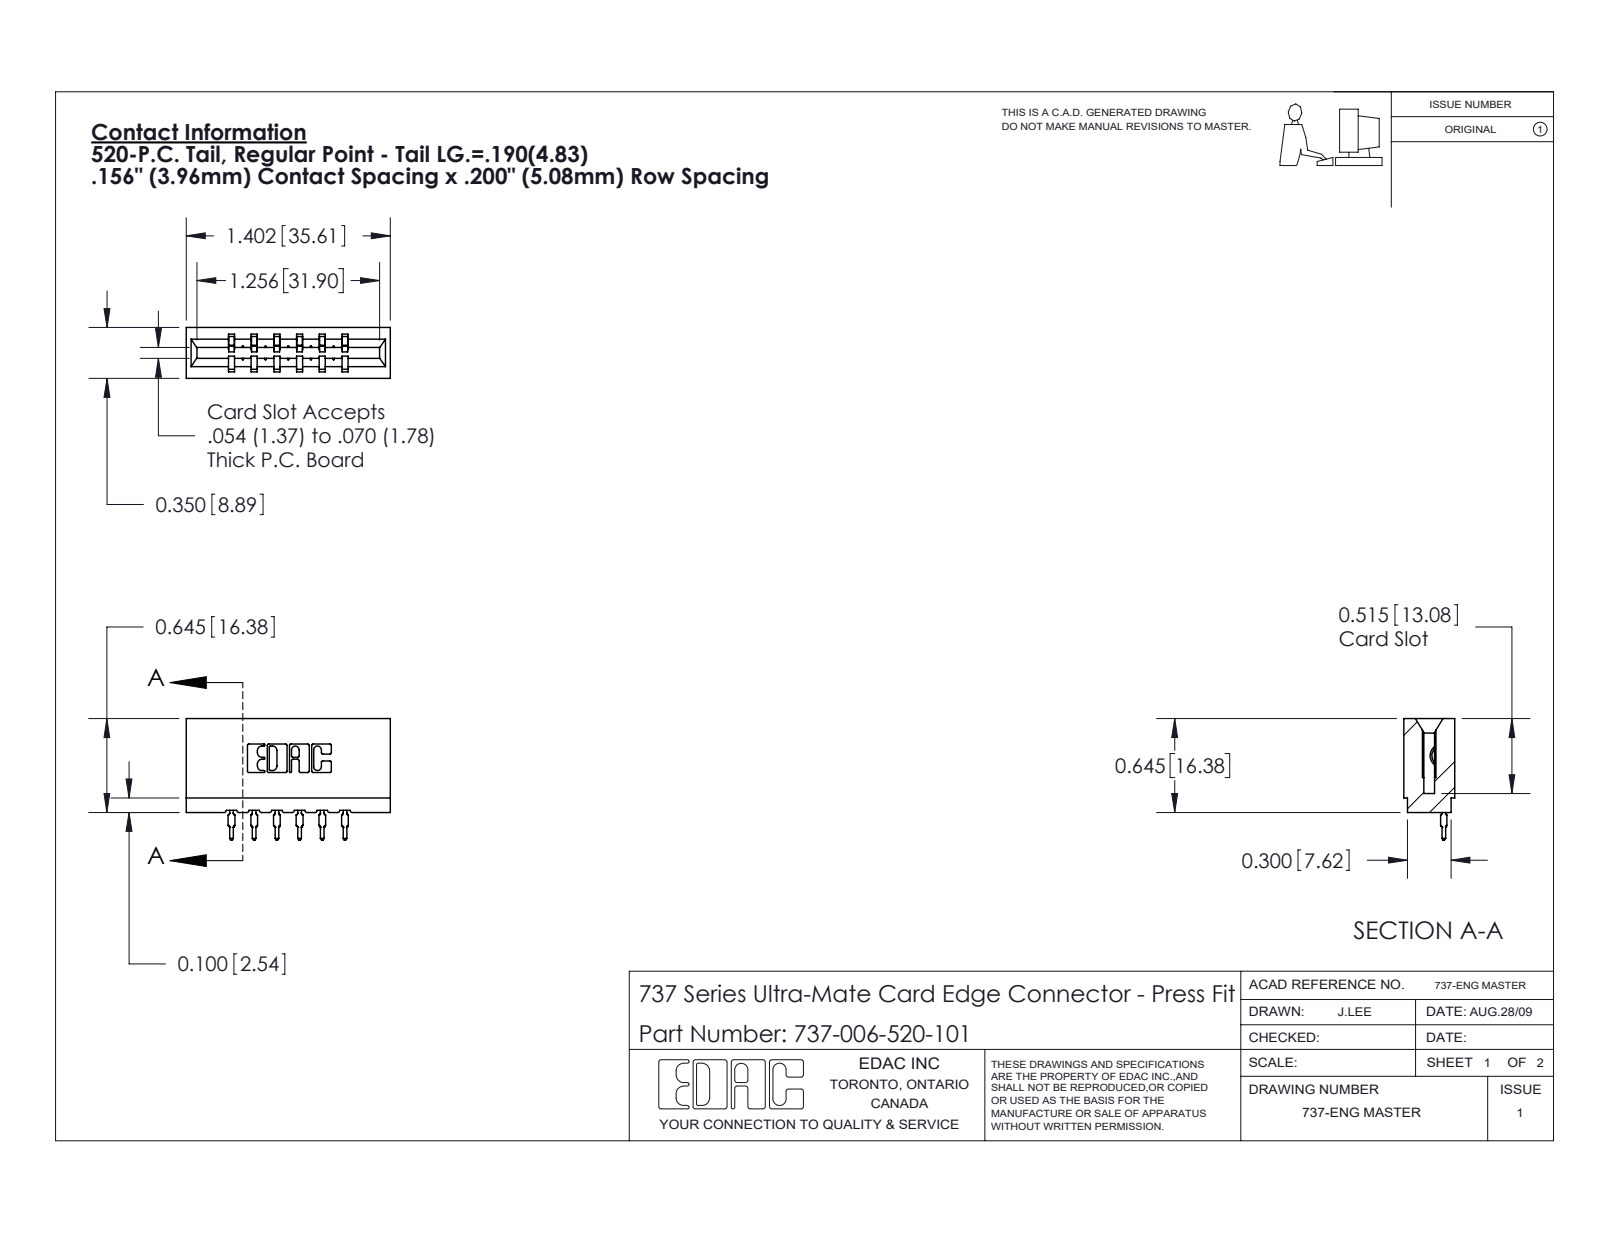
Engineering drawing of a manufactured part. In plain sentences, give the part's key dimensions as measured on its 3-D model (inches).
The part is named "745-292-001_520; 737-006-520-101; 737 Part_Insulator Option - 01". Its 3-D file was written by "SolidWorks 2020 (CONFIG_CONTROL_DESIGN)". It is 7 solids with 772 faces: 462 planar, 154 cylindrical and 156 other. Overall it measures 1.402 by 0.836 by 0.35 inches. Its volume is 0.225 cubic inches and its surface area 6.576 square inches. Partial cylindrical surfaces (rounded edges, fillets, slot ends): 22 of radius 0.01, 12 of radius 0.015, 12 of radius 0.021, 6 of radius 0.007, 6 of radius 0.031, 4 of radius 0.005, 4 of radius 0.011, 3 of radius 0.026. The main face-to-face distances are 0.156, 0.138, 0.212, 0.35, 0.312, 0.354, 0.198, 0.074, 0.468, 0.312.
